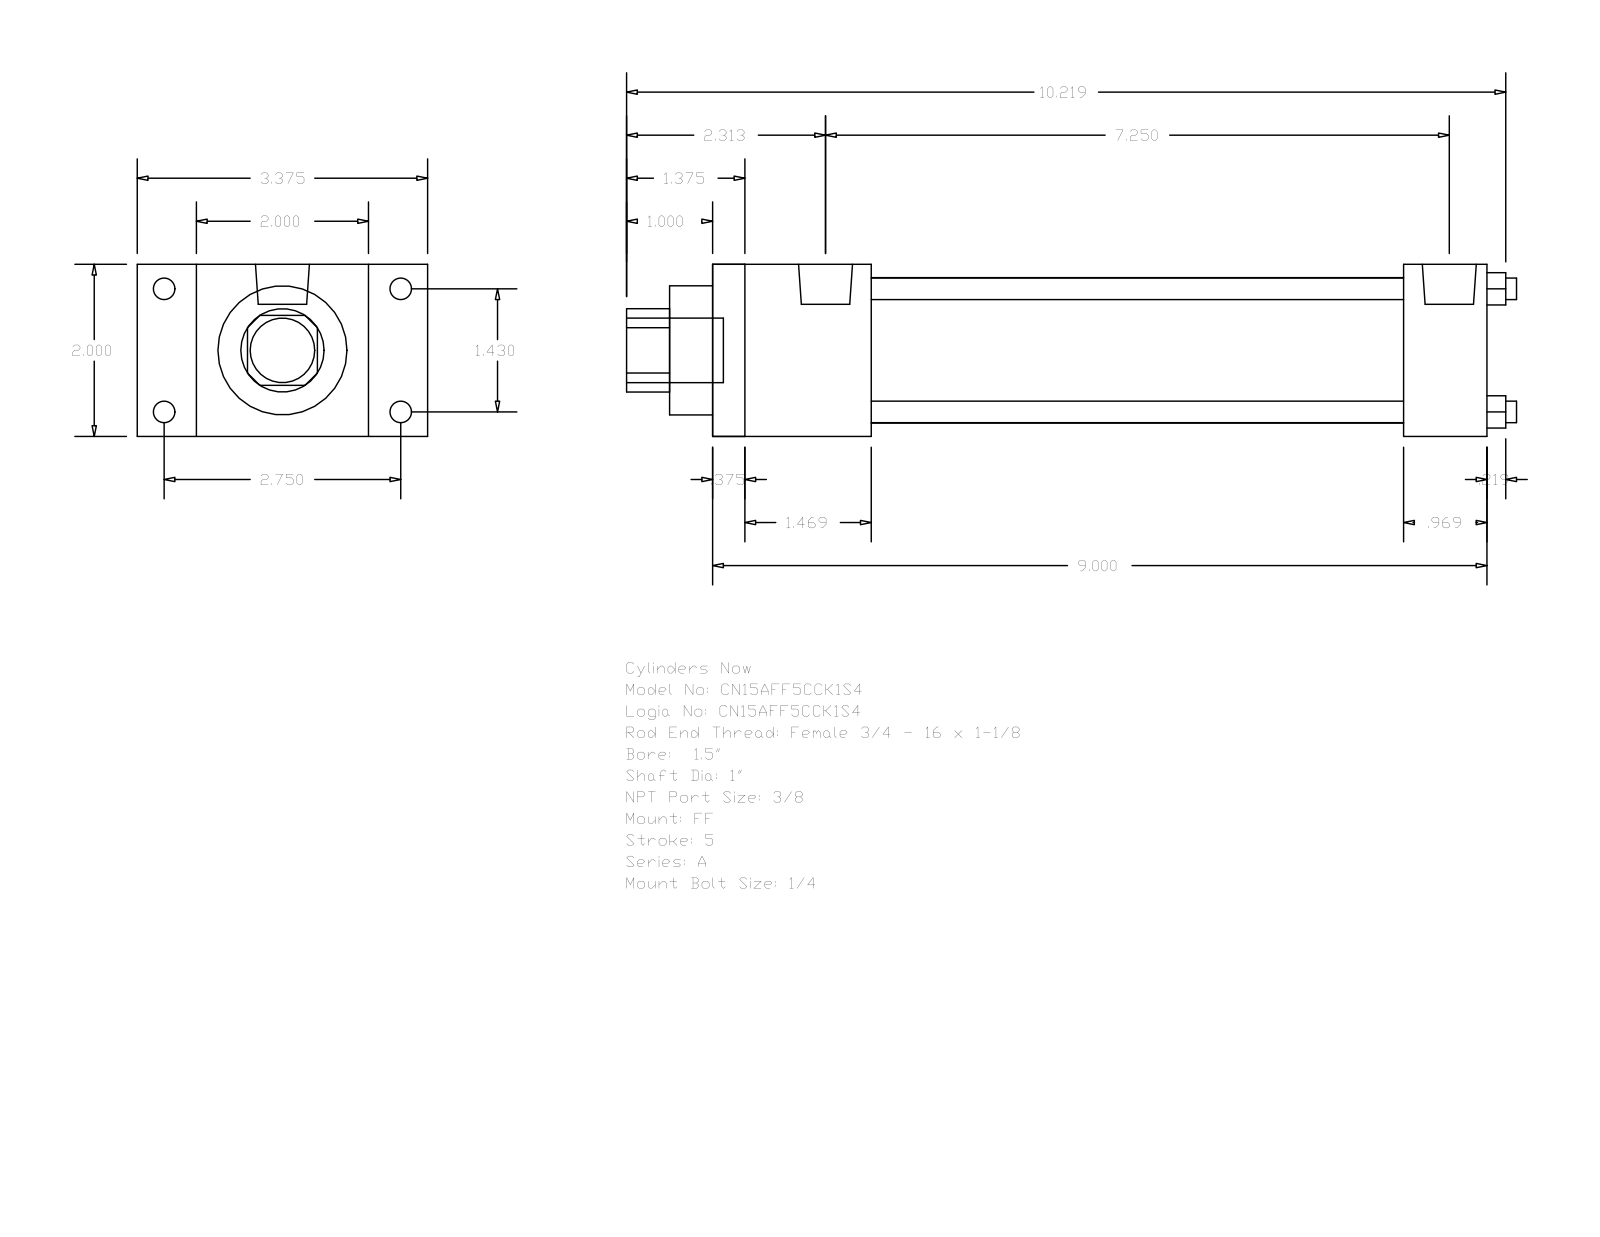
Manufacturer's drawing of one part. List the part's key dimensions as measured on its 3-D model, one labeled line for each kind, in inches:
Part name (STEP PRODUCT): A_FF__0150_1
STEP written by: GSSL Pune (CONFIG_CONTROL_DESIGN)
Units: inches
Bodies: 0 solids, 92 faces (64 planar, 28 cylindrical, 0 other)
Overall size (bounding box): 10.344 × 3.375 × 2
Round holes (diameter × count): ⌀0.25 ×4, ⌀1 ×1, ⌀1.5 ×1, ⌀1.69 ×1
Round bosses / shafts (diameter × count): ⌀0.25 ×4, ⌀0.219 ×4, ⌀0.627 ×2, ⌀0.75 ×1
Partial cylindrical surfaces — rounded edges, fillets, slot ends (radius × count): R0.484 ×1
Main face-to-face distances: 2, 9, 0.375, 8.625, 1.844, 8.031, 1.469, 7.656, 6.187, 7.156
Hole centre spacings: 1.011, 1.43, 2.022
